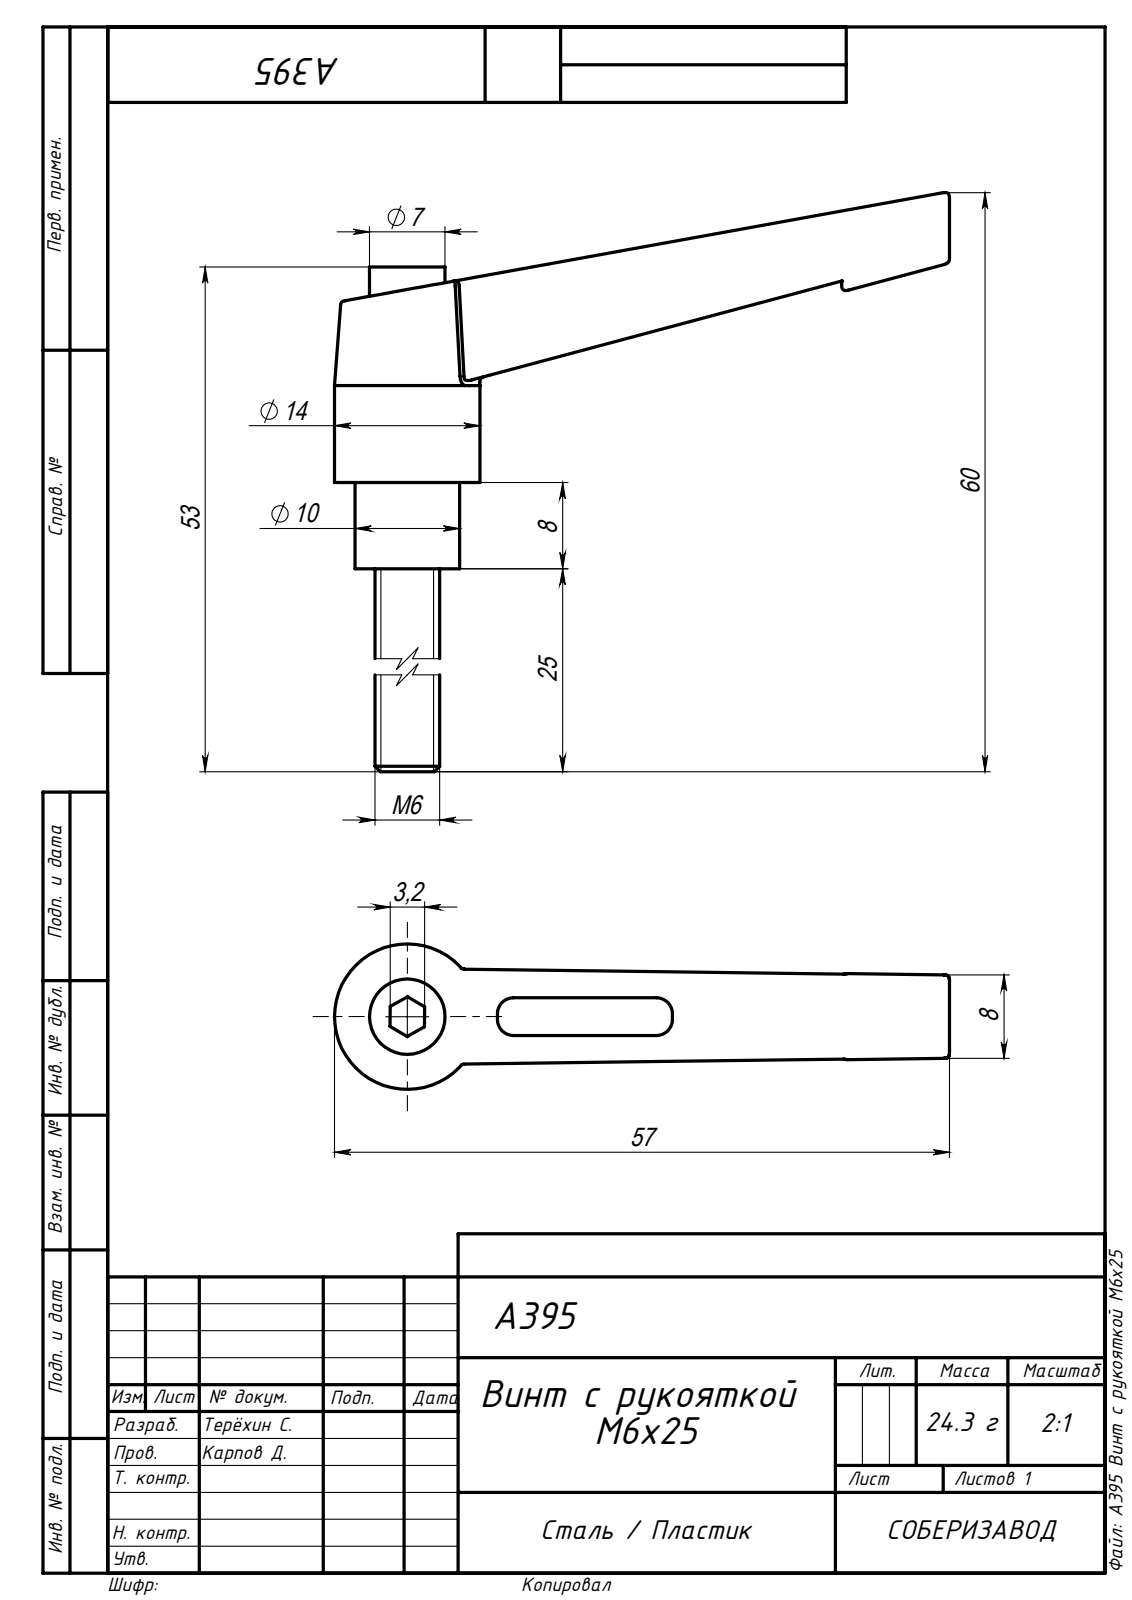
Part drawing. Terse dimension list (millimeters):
name: A395 Винт с рукояткой М6х25
written by: SolidWorks 2020 (AUTOMOTIVE_DESIGN)
unit: mm
bodies: 1 solid, 84 faces (29 planar, 12 cylindrical, 43 other)
size: 59.92 × 57.04 × 13.5
volume: 5 259 mm³; area: 3 571 mm²
bosses: 1× ⌀13.5, 1× ⌀9.7, 1× ⌀7, 1× ⌀6
rounds: 4× R1.5
face distances: 5.96, 8, 33.84, 28, 20, 25, 33, 53, 3.2, 50
